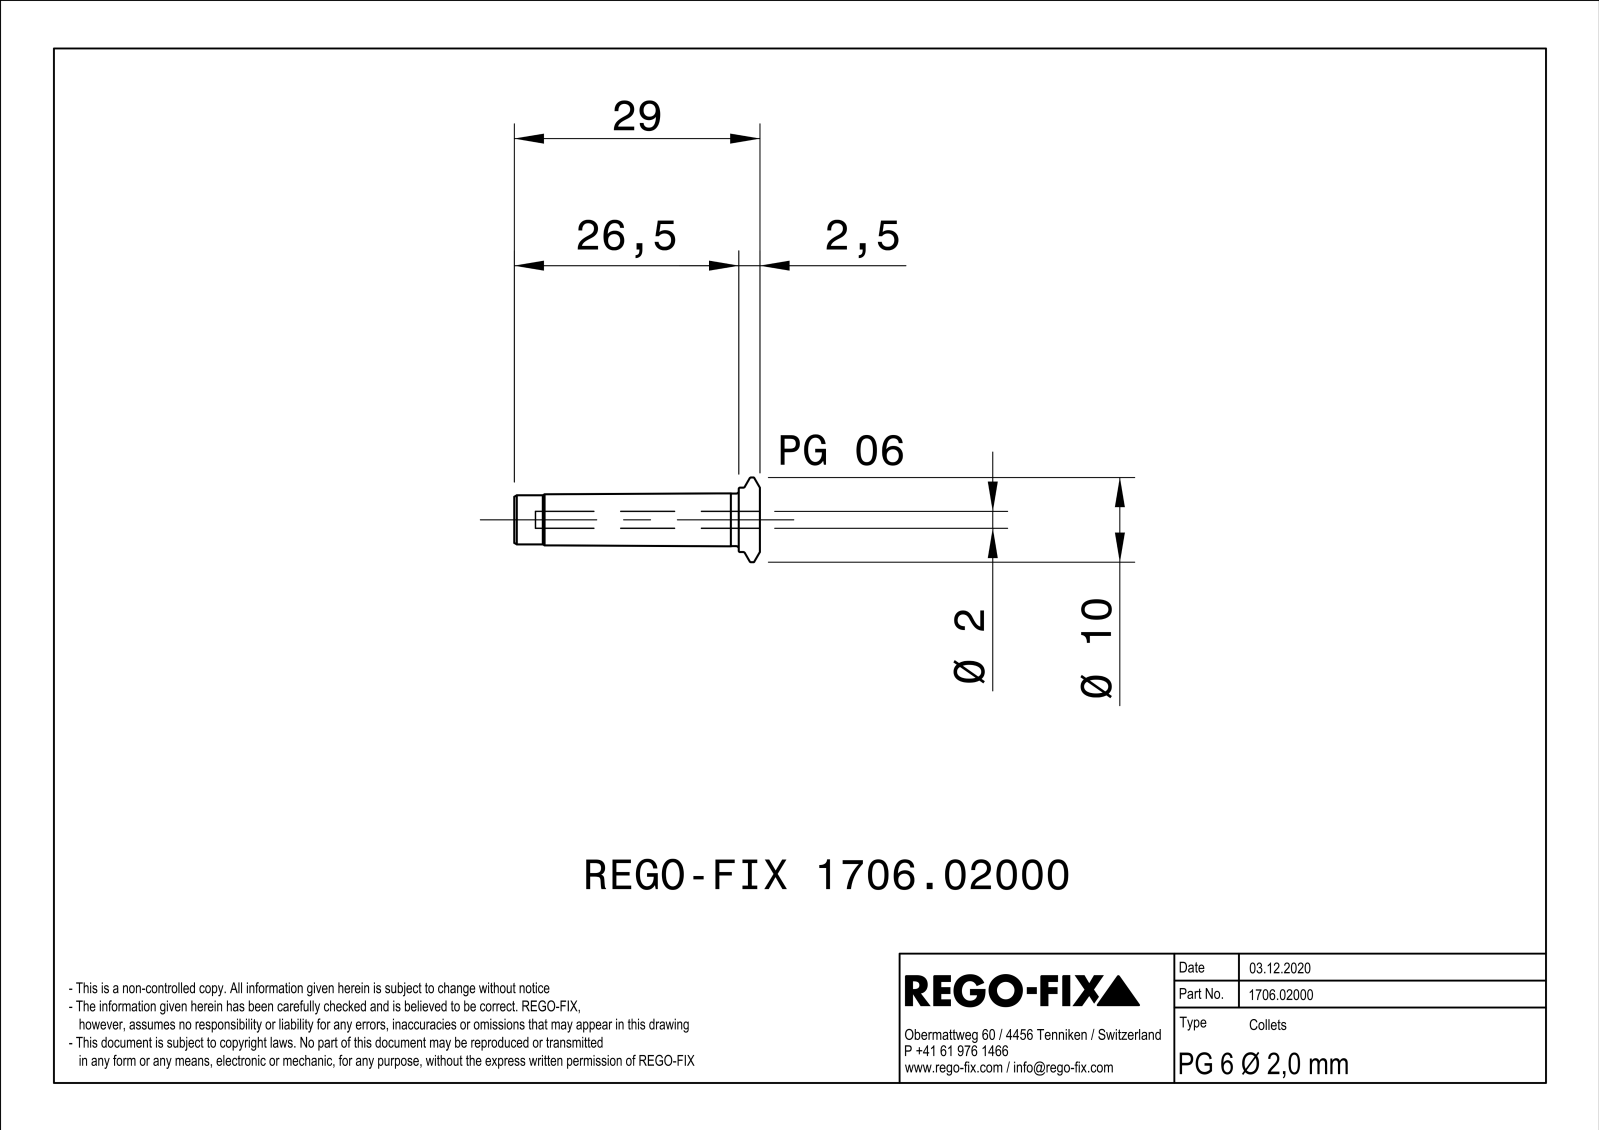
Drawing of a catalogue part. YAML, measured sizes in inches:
part_name: "NOCUT"
step_written_by: "SIEMENS PLM Software Solid Edge ST10 (AUTOMOTIVE_DESIGN)"
units: inches
bodies: {solids: 1, faces: 61, planar: 17, cylindrical: 12, other: 32}
overall_size: [1.142, 0.394, 0.393]
volume: 0.046
surface_area: 1.669
round_holes:
  - {diameter: 0.079, count: 1}
  - {diameter: 0.136, count: 1}
round_bosses_or_shafts:
  - {diameter: 0.394, count: 1}
  - {diameter: 0.299, count: 1}
  - {diameter: 0.244, count: 1}
  - {diameter: 0.228, count: 1}
face_to_face_distances: [0.018, 0.018, 1.142, 0.098, 1.043]
